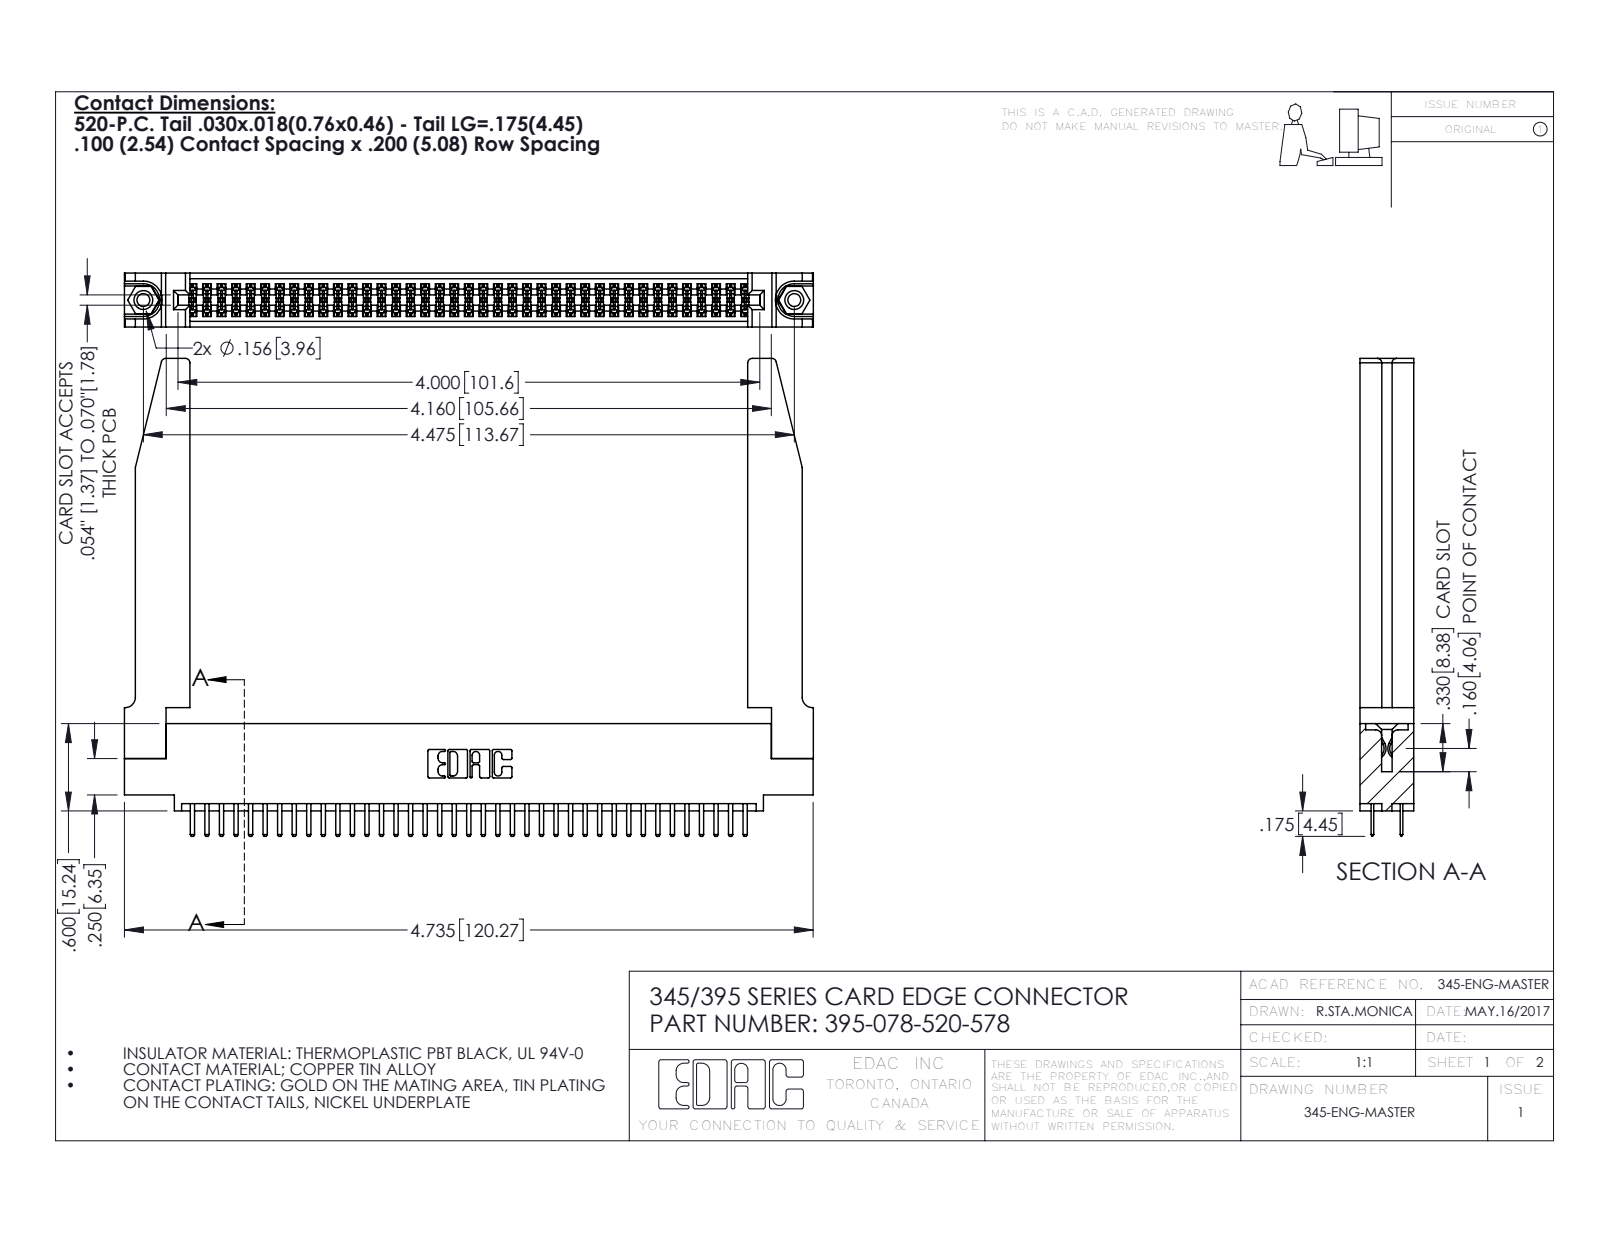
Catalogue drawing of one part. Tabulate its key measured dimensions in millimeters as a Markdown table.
| quantity | value |
| --- | --- |
| part name | 395-078-520-578; 345-250-001_345-250-001-102; 345 Part_0.110 Offset - 0.156 Dia-TH; 345-292-001_345-293-120 (+1 more) |
| STEP written by | SolidWorks 2016 (CONFIG_CONTROL_DESIGN) |
| units | millimeters |
| bodies | 83 solids, 4576 faces (2956 planar, 1568 cylindrical, 52 other) |
| overall size | 120.3 × 83.4 × 9.4 |
| volume | 19 320 mm³ |
| surface area | 23 870 mm² |
| round holes (diameter × count) | 2.3 × 2, 3.2 × 2, 4 × 2, 1.6 × 1 |
| round bosses / shafts (diameter × count) | 3.9 × 2 |
| partial cylindrical surfaces (radius × count) | 0.2 × 117, 0.3 × 82, 0.3 × 22, 0.8 × 8, 0.2 × 6, 0.8 × 6, 0.7 × 3, 0.4 × 2 |
| main face-to-face distances | 9.4, 1.8, 7.6, 5.1, 2.5, 6.9, 0.6, 5.7, 0.6, 4.4 |
| hole center spacings | 6.9, 107.7, 113.7 |
